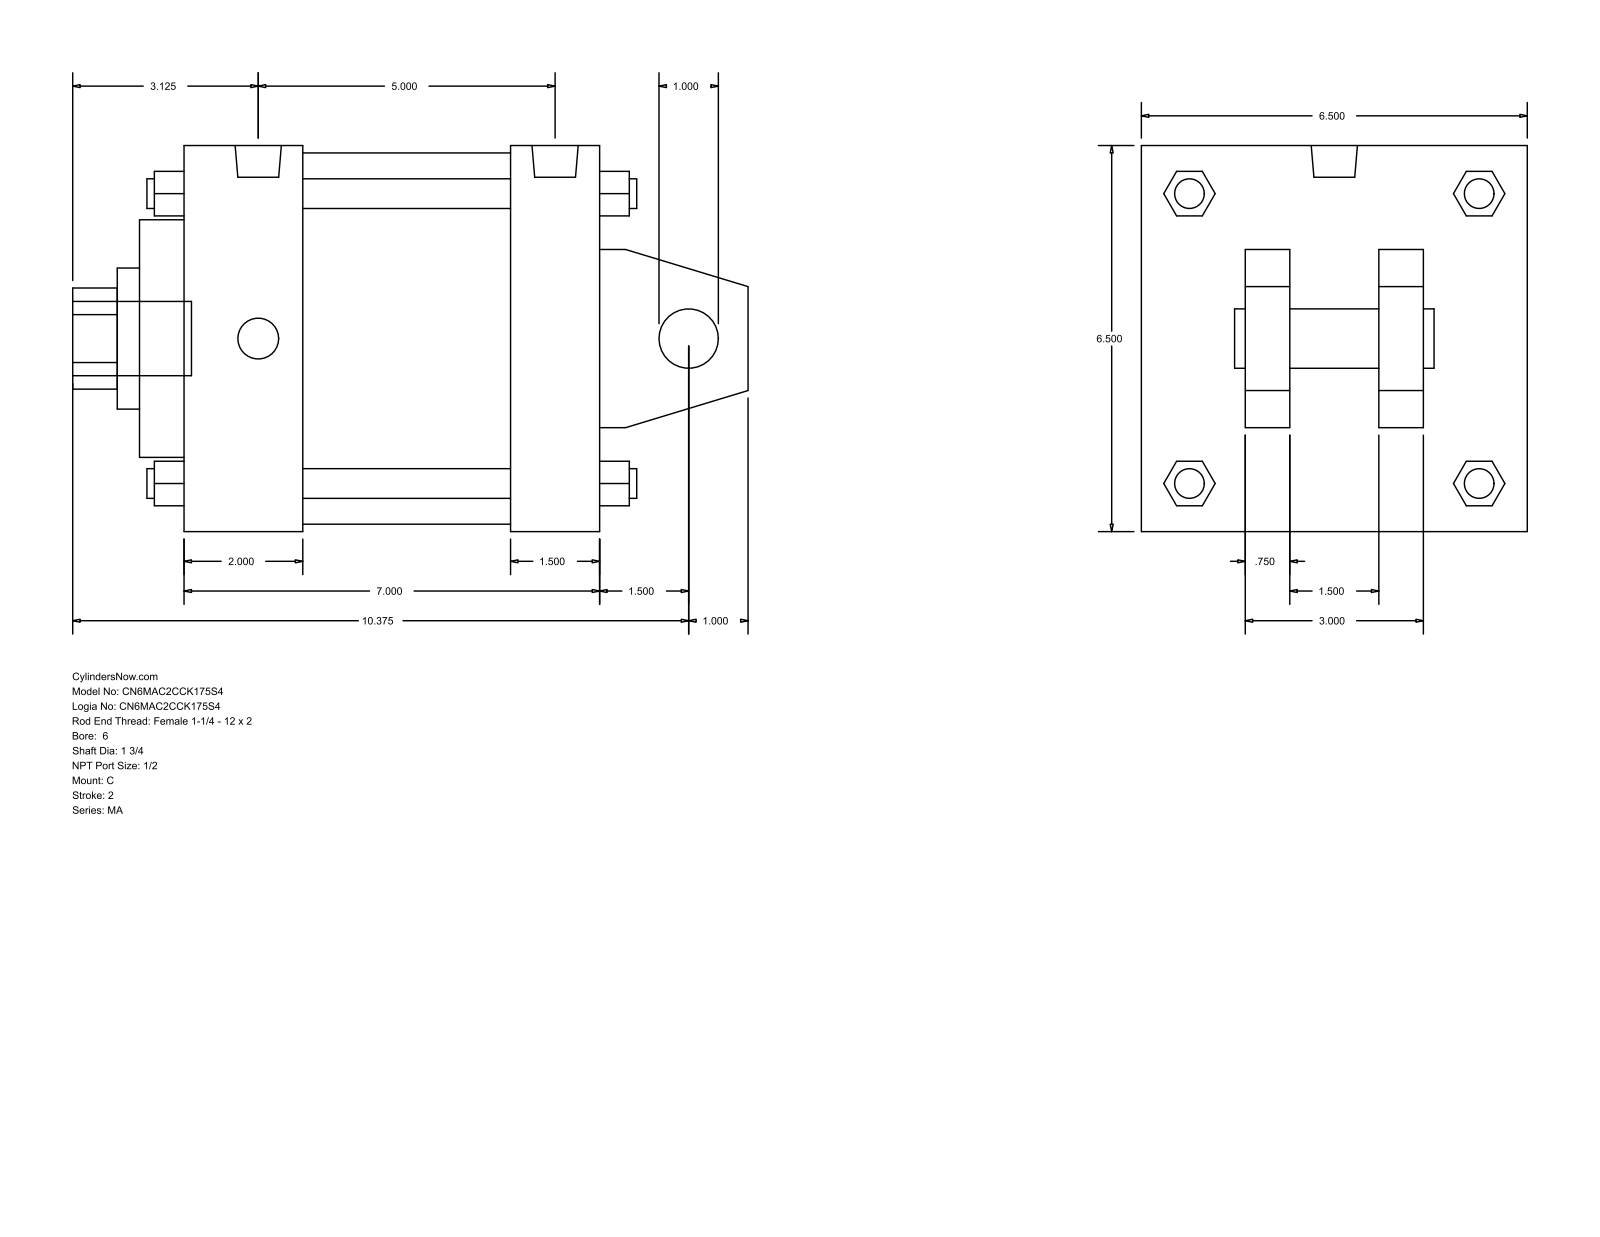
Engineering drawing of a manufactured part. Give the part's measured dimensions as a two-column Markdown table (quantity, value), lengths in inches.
| quantity | value |
| --- | --- |
| part name | MA_C__0600_1.75 |
| STEP written by | GSSL Pune (CONFIG_CONTROL_DESIGN) |
| units | inches |
| bodies | 0 solids, 141 faces (109 planar, 32 cylindrical, 0 other) |
| overall size | 11.375 × 6.5 × 6.5 |
| round holes (diameter × count) | 1 × 1, 1.75 × 1, 2.375 × 1, 4 × 1, 6.25 × 1 |
| round bosses / shafts (diameter × count) | 0.687 × 4, 0.5 × 4, 0.778 × 2, 1.25 × 1 |
| partial cylindrical surfaces (radius × count) | 0.852 × 1 |
| main face-to-face distances | 6.5, 7, 0.75, 2.5, 4, 2, 1.75, 4.75, 5.5, 2.25 |
